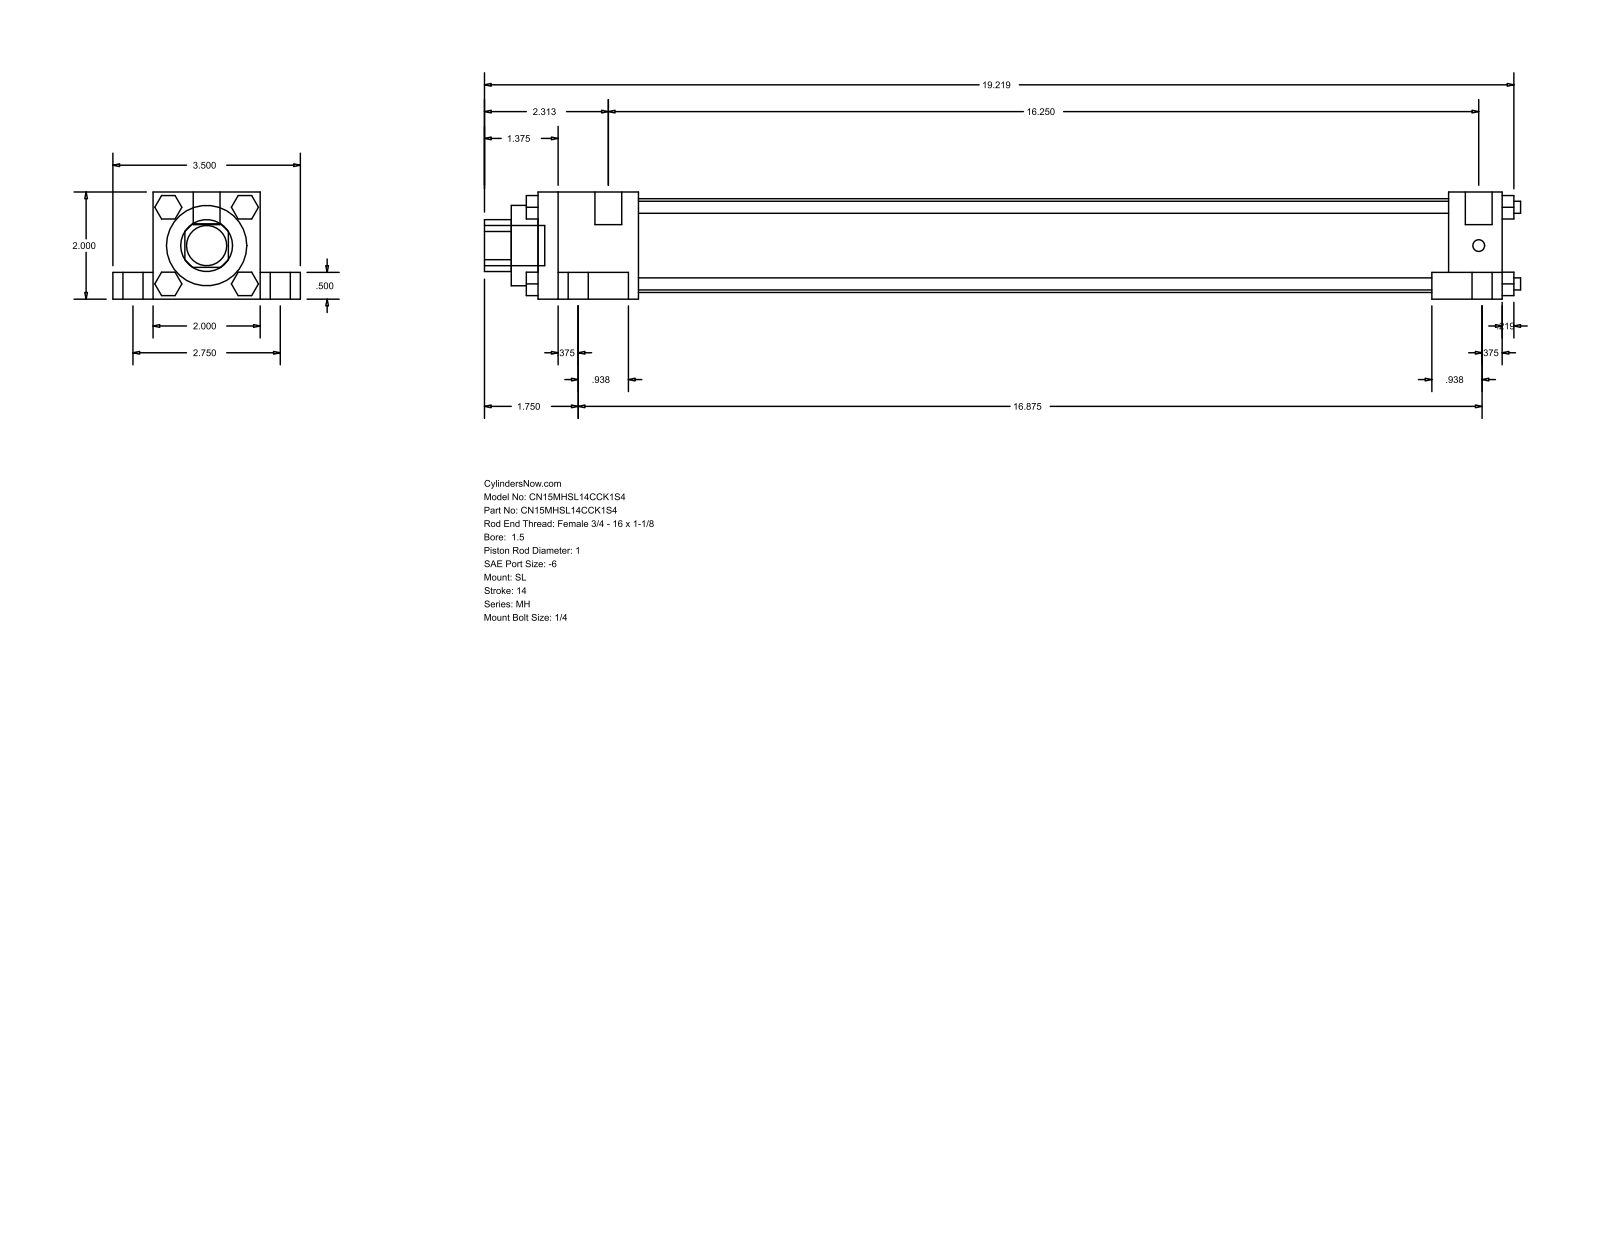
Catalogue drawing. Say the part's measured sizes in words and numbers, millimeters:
The part is named "MH_SL__0150_1". Its 3-D file was written by "GSSL Pune (CONFIG_CONTROL_DESIGN)". It is 0 solids with 148 faces: 112 planar, 36 cylindrical and 0 other. Overall it measures 491.33 by 88.9 by 50.8 millimeters. Round holes: 1 of diameter 25.4, 1 of diameter 38.1, 1 of diameter 44.45. Round bosses or shafts: 4 of diameter 15.88, 4 of diameter 9.53, 4 of diameter 5.71, 4 of diameter 5.56, 2 of diameter 12.7, 1 of diameter 19.05. Partial cylindrical surfaces (rounded edges, fillets, slot ends): 1 of radius 12.29. The main face-to-face distances are 50.8, 12.7, 38.1, 19.05, 69.85, 457.2, 25.4, 9.52, 33.34, 414.34.
